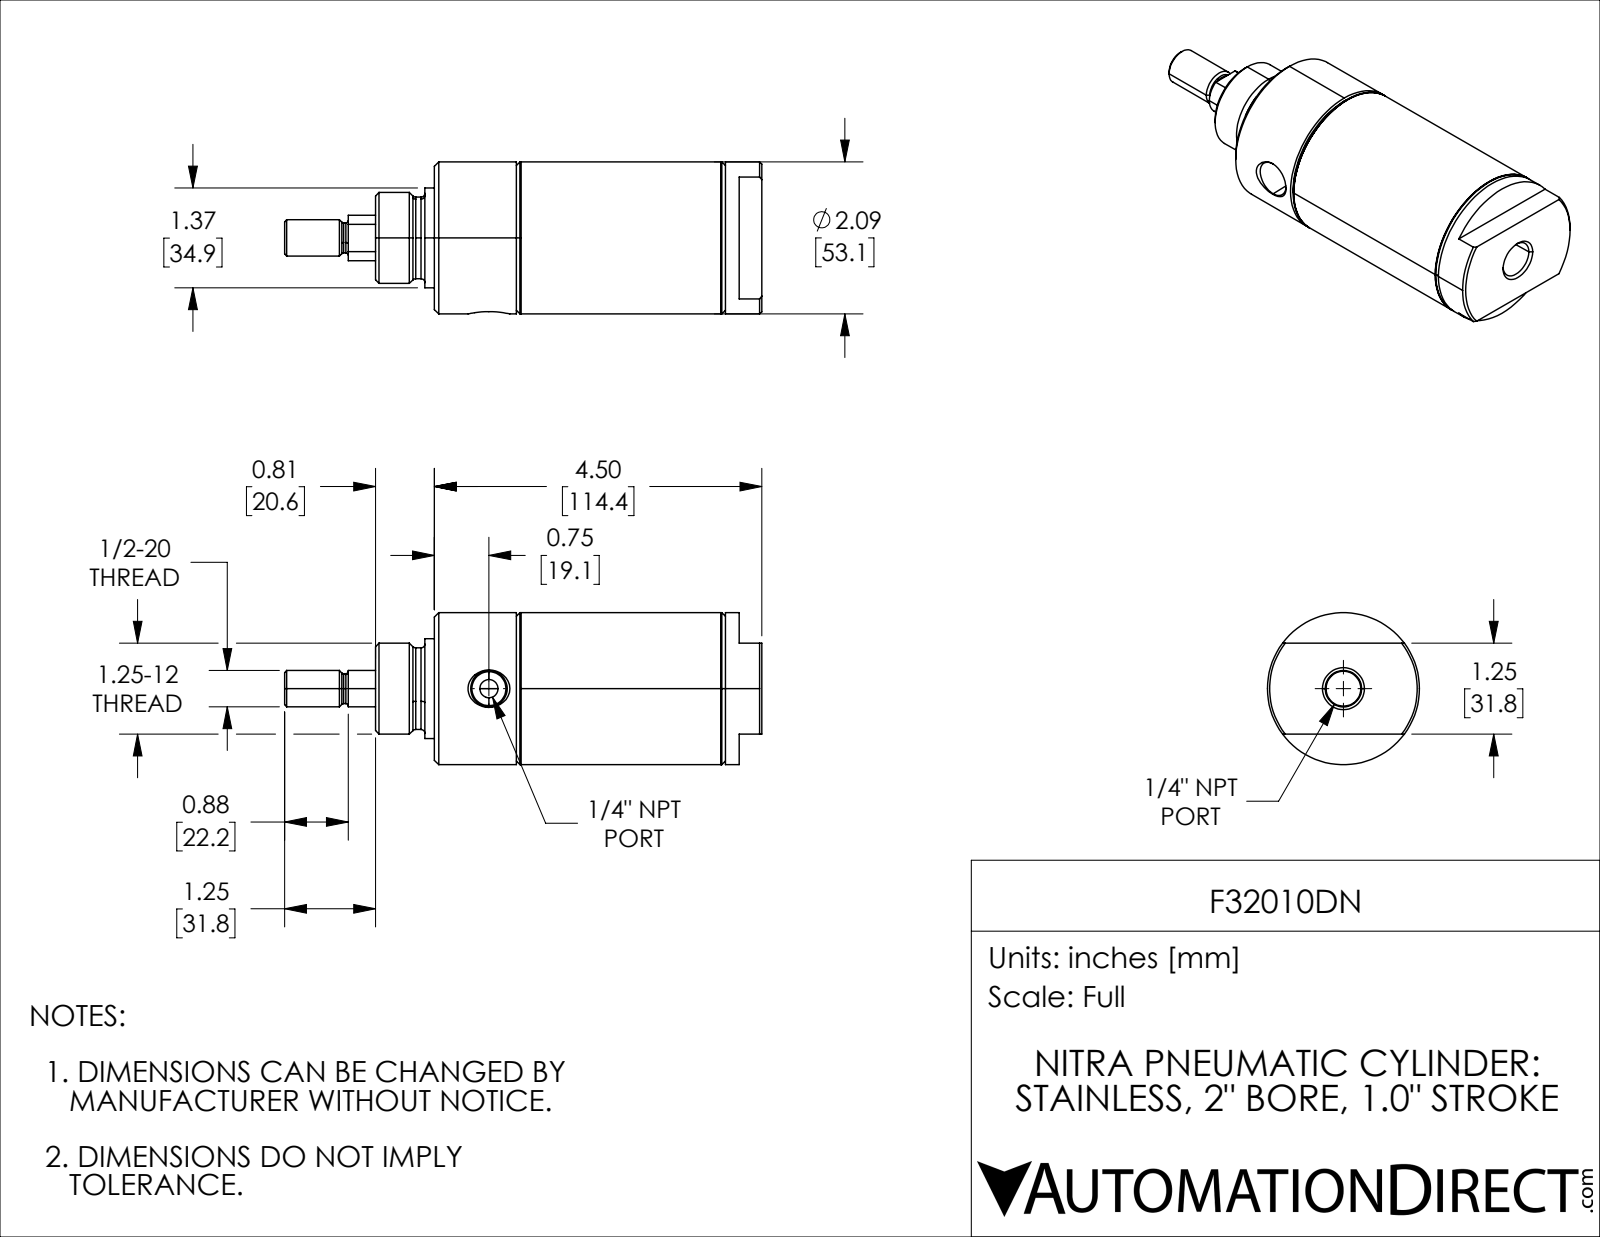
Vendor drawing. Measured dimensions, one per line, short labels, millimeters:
name: F32010DN_3; F32010DN_7; F32010DN_5; F32010DN_9 (+1 more)
written by: SolidWorks 2021 (CONFIG_CONTROL_DESIGN)
unit: mm
bodies: 4 solids, 133 faces (25 planar, 46 cylindrical, 62 other)
size: 166.68 × 53.09 × 53.09
volume: 210 027 mm³; area: 64 868 mm²
holes: 1× ⌀6.35, 1× ⌀12.18, 1× ⌀16.52, 1× ⌀31.75, 1× ⌀49.05
bosses: 1× ⌀53.09, 1× ⌀51.16, 1× ⌀34.87, 1× ⌀28.51, 1× ⌀15.88, 1× ⌀12.7, 1× ⌀10.46
face distances: 30.18, 25.4, 55.58, 76.2, 50.8, 20.62, 55.57, 30.17, 20.63, 38.15
